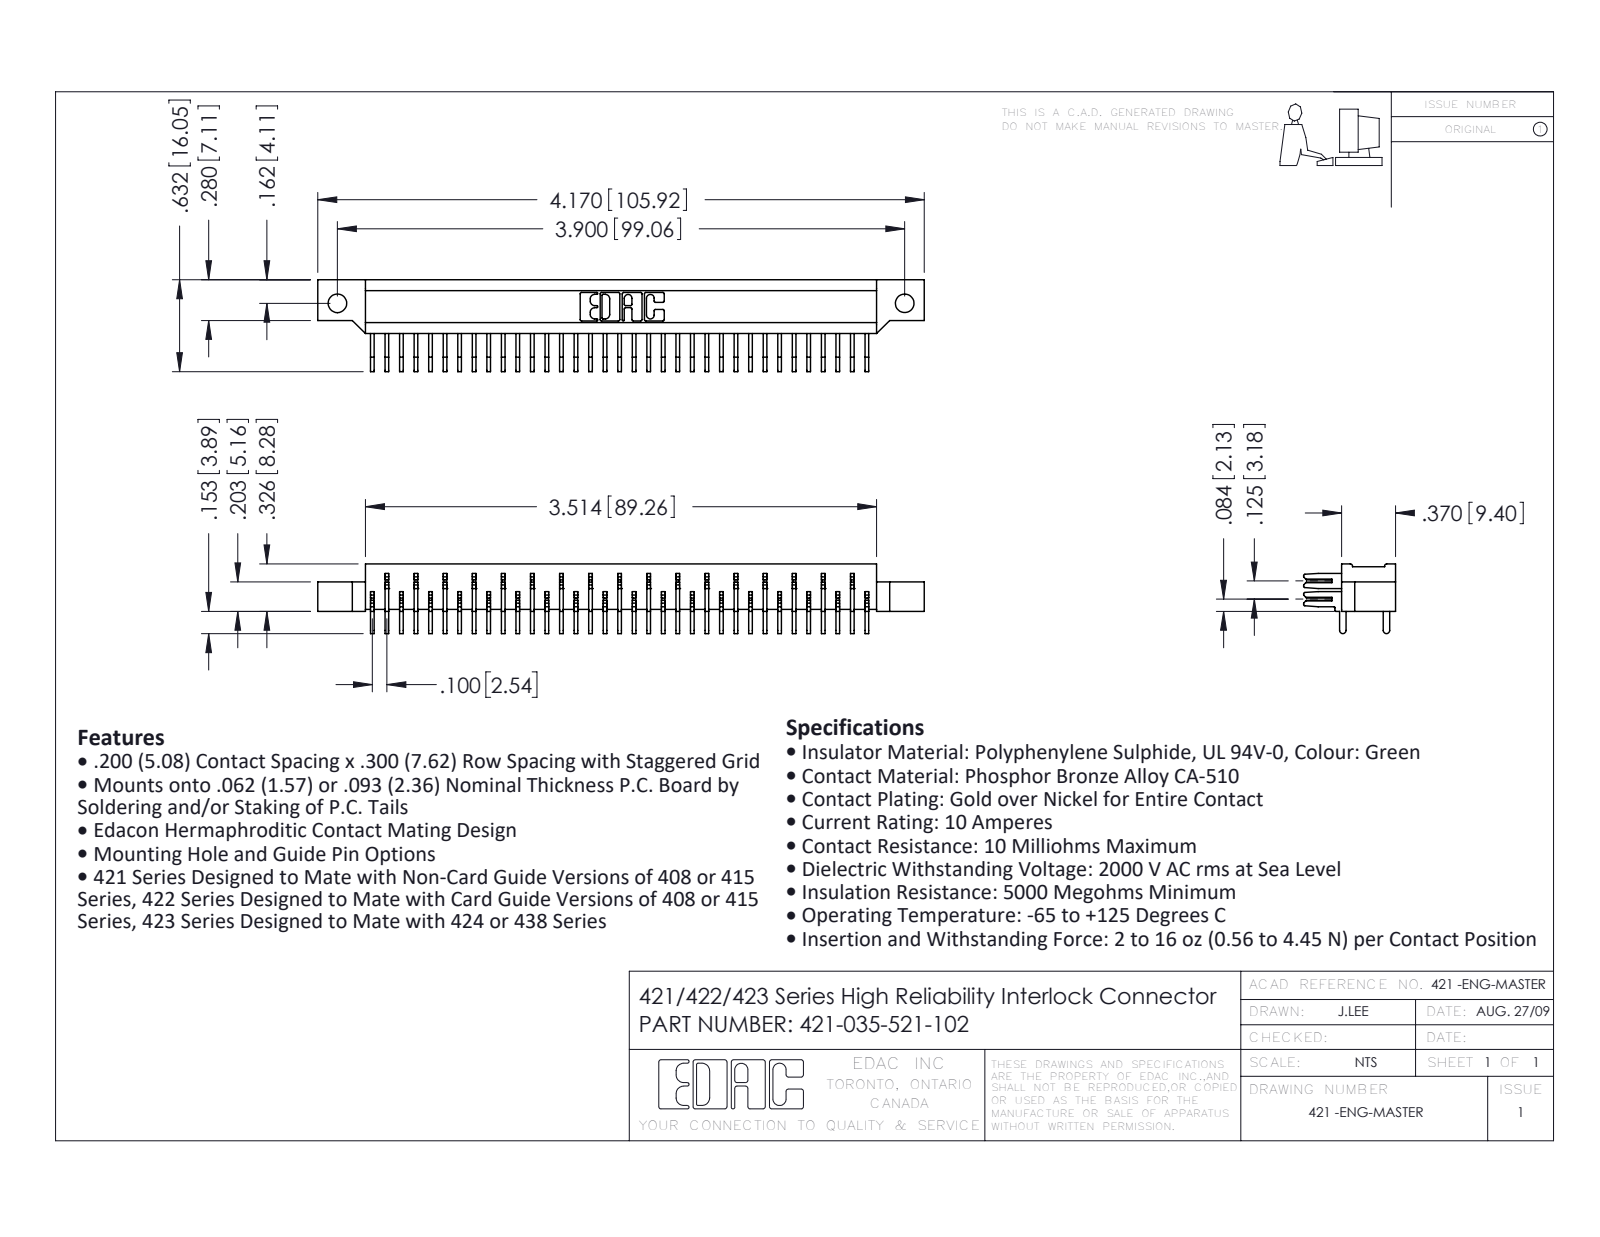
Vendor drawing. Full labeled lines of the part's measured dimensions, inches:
Part name (STEP PRODUCT): 421-290-002_121; 421-035-521-102; 421-290-001_121; 421 Part_35
STEP written by: SolidWorks 2016 (CONFIG_CONTROL_DESIGN)
Units: inches
Bodies: 36 solids, 1196 faces (976 planar, 220 cylindrical, 0 other)
Overall size (bounding box): 4.17 × 0.632 × 0.479
Volume: 0.453 in³ · Surface area: 18.64 in²
Round holes (diameter × count): ⌀0.128 ×2
Partial cylindrical surfaces — rounded edges, fillets, slot ends (radius × count): R0.01 ×22, R0.007 ×6, R0.031 ×6, R0.007 ×4, R0.01 ×4, R0.026 ×3, R0.015 ×2, R0.022 ×2
Main face-to-face distances: 0.2, 0.4, 0.6, 0.8, 1, 1.2, 1.4, 1.6, 1.8, 2
Hole centre spacings: 3.9
